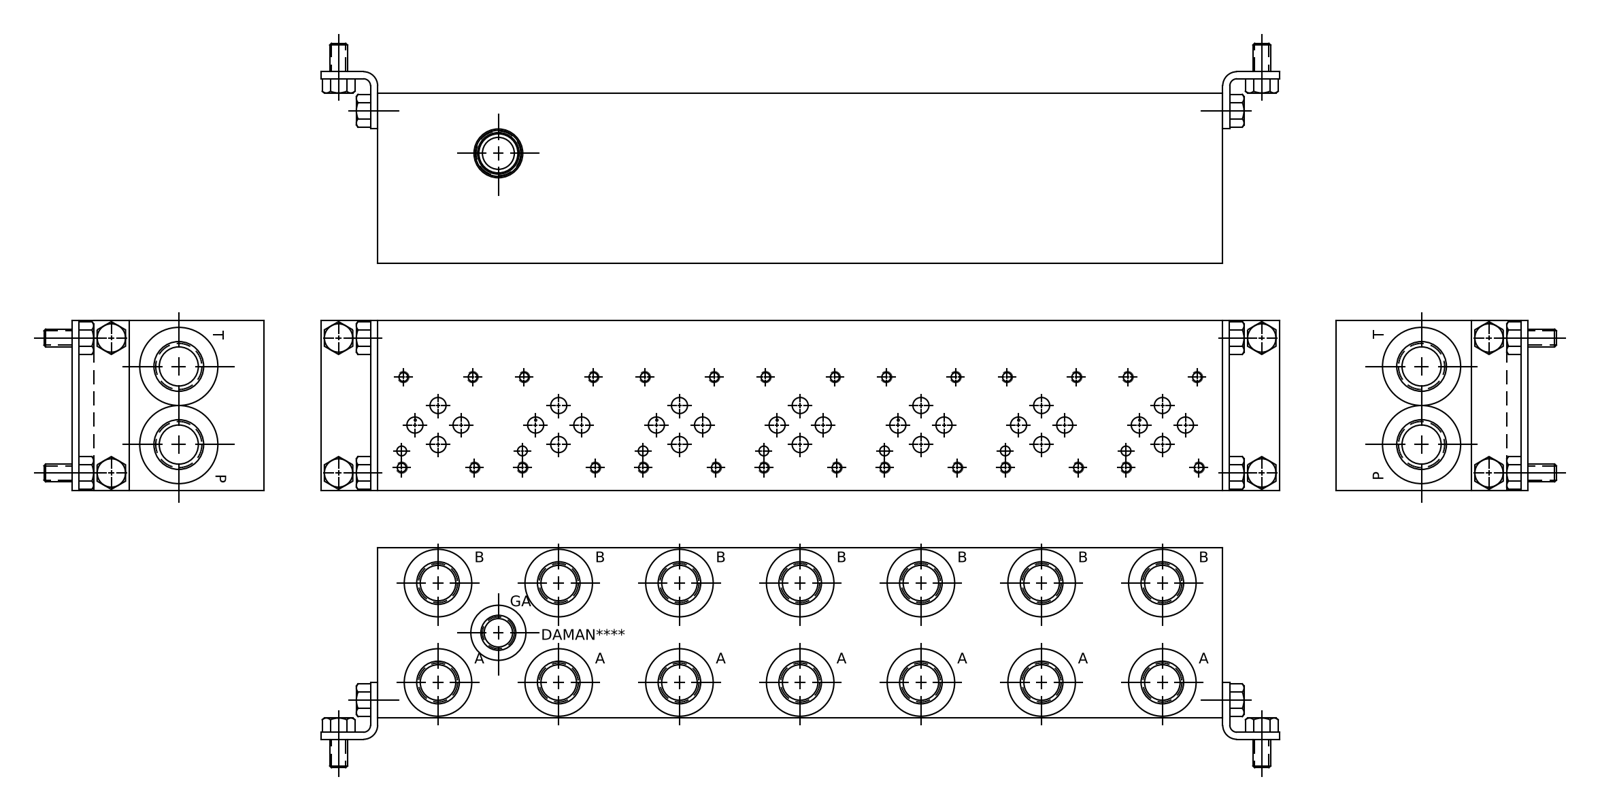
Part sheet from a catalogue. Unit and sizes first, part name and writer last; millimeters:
Units: millimetres
Overall size (bounding box): 377.82 × 76.2 × 76.2
Round holes (diameter × count): ⌀3.78 ×28, ⌀4.83 ×28, ⌀7.14 ×21, ⌀15.88 ×14, ⌀17.5 ×14, ⌀19.05 ×14, ⌀19.25 ×14, ⌀30.63 ×14, ⌀3.96 ×7, ⌀6.35 ×7, ⌀6.53 ×2, ⌀7.92 ×2
Main face-to-face distances: 76.2, 0.79, 75.41, 377.82, 377.04, 0.78, 376.25, 377.03, 14.27, 61.14
Hole centre spacings: 107.95, 53.98, 215.9, 53.97, 161.93, 118.61, 116.74, 161.92
Volume: 2 026 000 mm³ · Surface area: 167 885 mm²
Bodies: 1 solid, 1119 faces (535 planar, 200 cylindrical, 384 other)
Part name (STEP PRODUCT): Part_AD03P072S_S_3D
STEP written by: Autodesk Inventor 2020 (AUTOMOTIVE_DESIGN)
